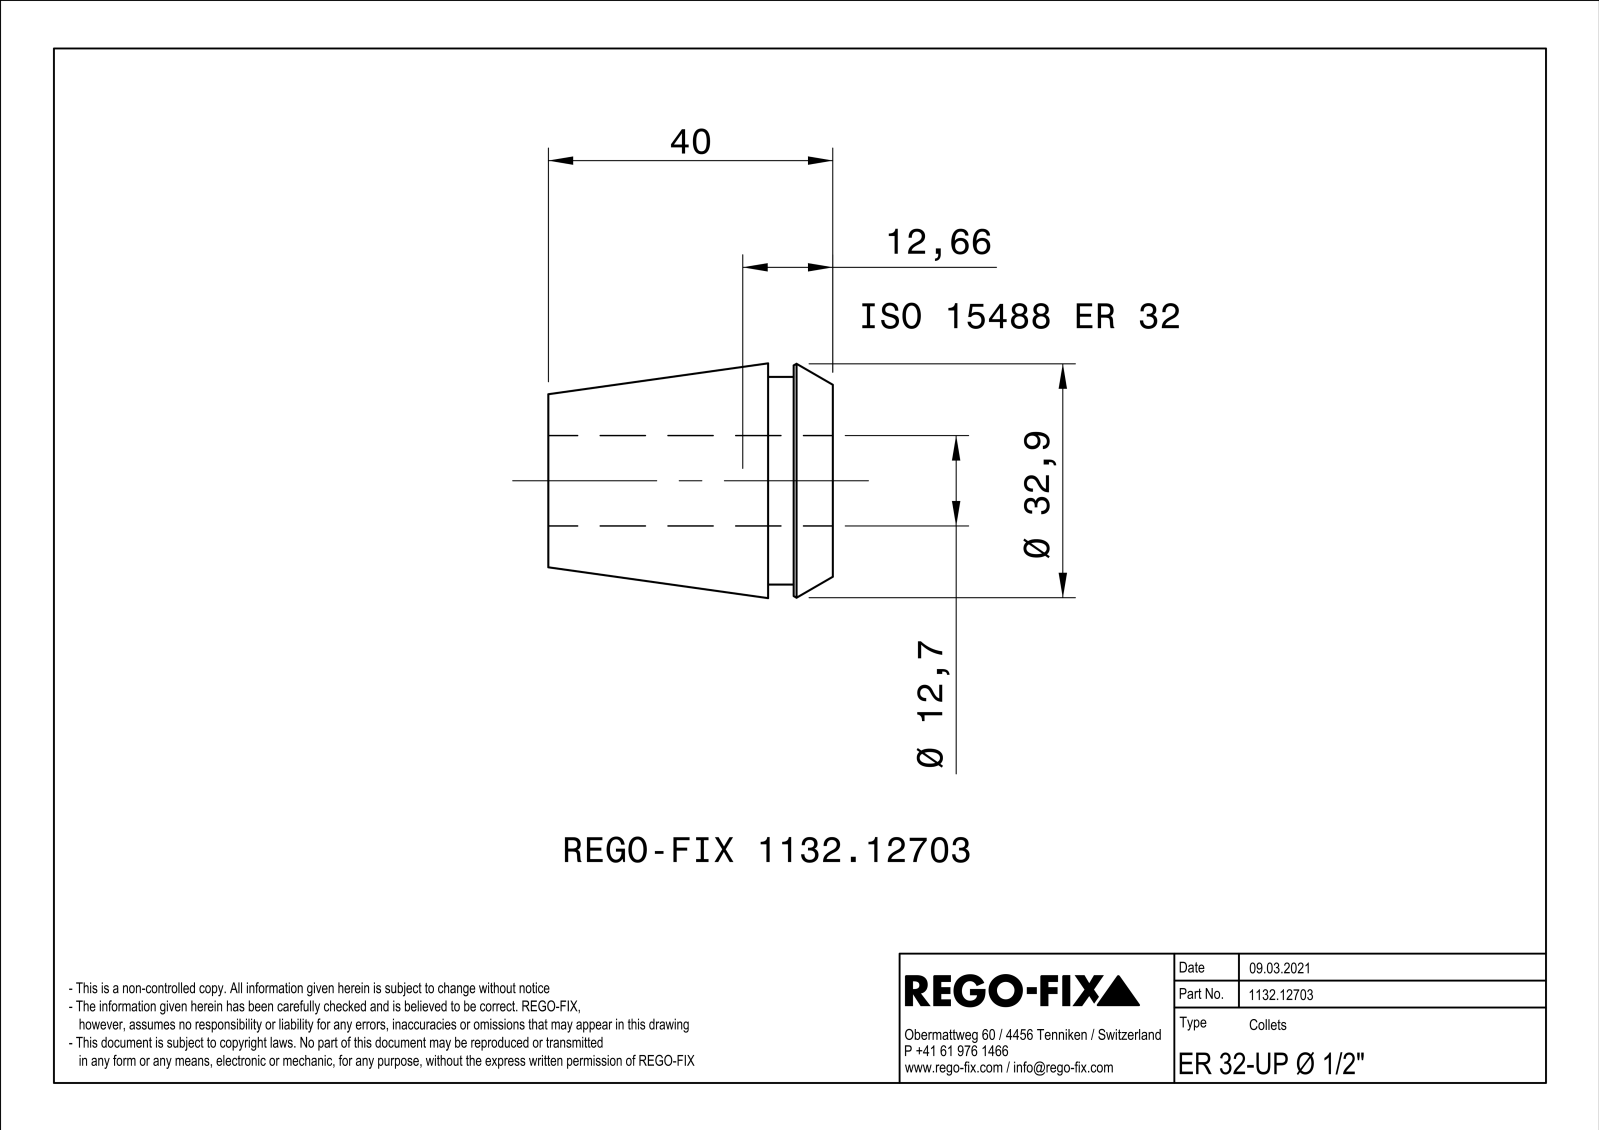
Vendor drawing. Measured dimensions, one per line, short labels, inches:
name: NOCUT
written by: SIEMENS PLM Software Solid Edge ST10 (AUTOMOTIVE_DESIGN)
unit: in
bodies: 1 solid, 209 faces (88 planar, 41 cylindrical, 80 other)
size: 1.575 × 1.298 × 1.298
volume: 1.022 in³; area: 22.45 in²
holes: 1× ⌀0.5
bosses: 1× ⌀1.15
rounds: 20× R0.016
face distances: 0.039, 1.575, 0.358, 1.217, 0.217, 0.142, 1.358, 0.236, 0.02, 0.122
